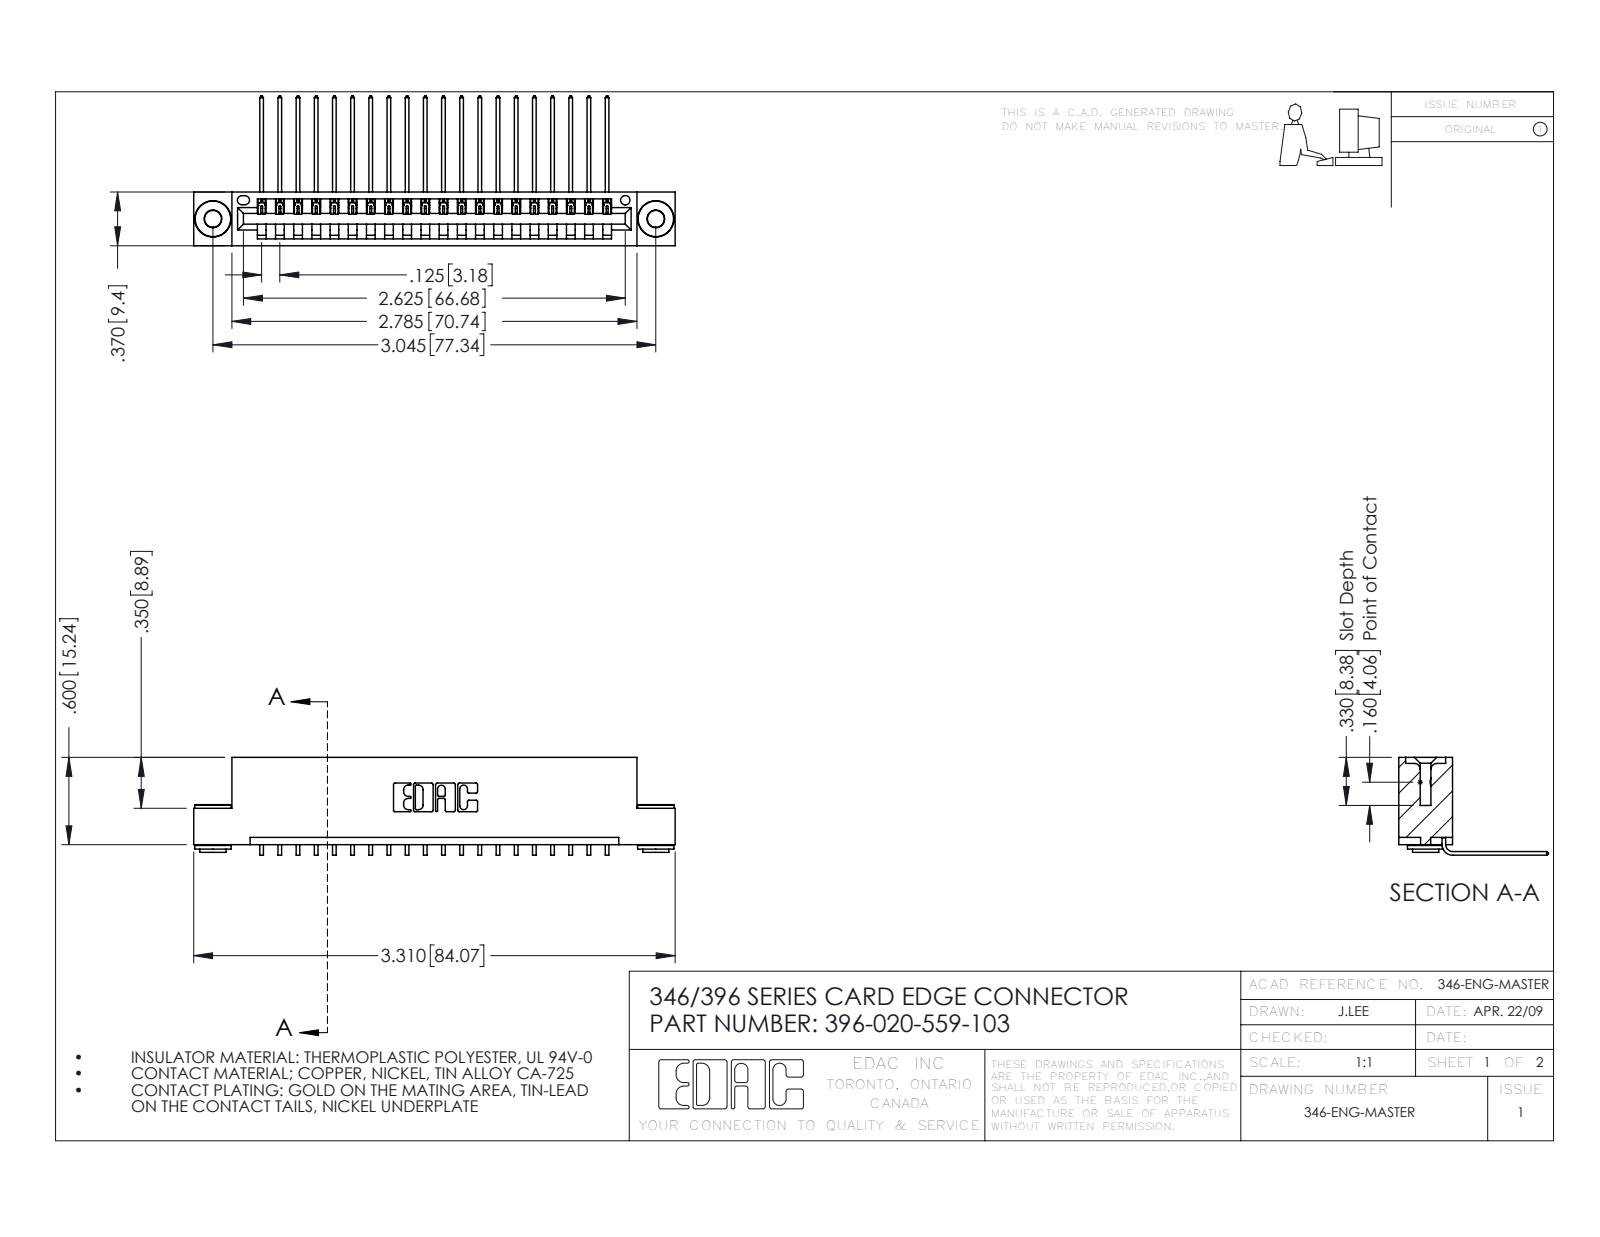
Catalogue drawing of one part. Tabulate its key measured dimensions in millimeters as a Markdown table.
| quantity | value |
| --- | --- |
| part name | 396-020-559-103; 346 Part_Flush Mounting Lugs - 0.156 Dia-TH; 345-292-001_558 559 Tail - 1; 345-250-002_345-250-002-102 |
| STEP written by | SolidWorks 2016 (CONFIG_CONTROL_DESIGN) |
| units | millimeters |
| bodies | 23 solids, 1360 faces (926 planar, 426 cylindrical, 8 other) |
| overall size | 84.1 × 26.2 × 17.1 |
| volume | 7 980 mm³ |
| surface area | 10 350 mm² |
| round holes (diameter × count) | 2.9 × 2, 4 × 2, 1.6 × 1 |
| round bosses / shafts (diameter × count) | 6.4 × 2, 4.6 × 2, 3.5 × 2 |
| partial cylindrical surfaces (radius × count) | 0.2 × 40, 0.3 × 22, 0.2 × 6, 0.8 × 6, 0.7 × 3, 0.8 × 2, 1 × 2, 0.4 × 1 |
| main face-to-face distances | 1.2, 8.2, 9.4, 6.4, 0.6, 1.8, 7.6, 3.8, 5.6, 2.5 |
| hole center spacings | 6.2, 72.1, 77.3 |
